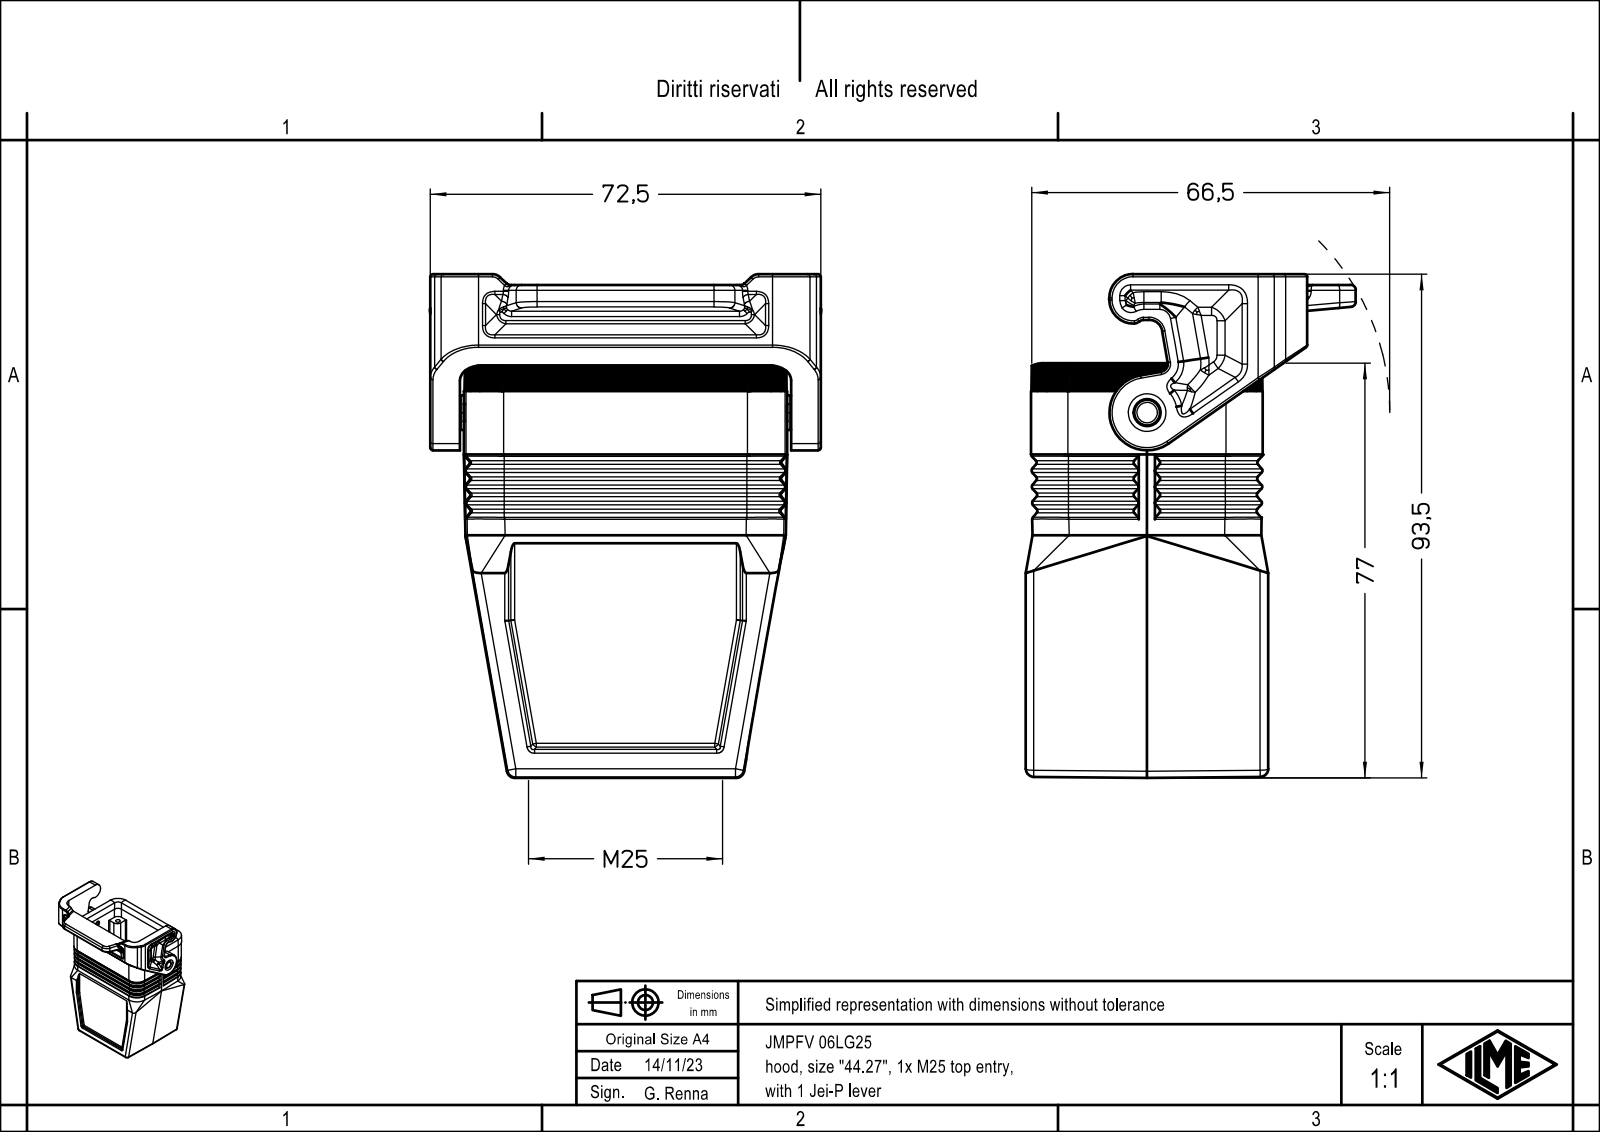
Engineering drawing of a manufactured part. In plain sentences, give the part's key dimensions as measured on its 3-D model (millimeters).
The part is named "JMPFV 06LG25". Its 3-D file was written by "Creo Elements/Direct Modeling 20.1B 02-Apr-2019 (C) Parametric Technology GmbH (AUTOMOTIVE_DESIGN)". It is 1 solid with 849 faces: 248 planar, 279 cylindrical and 322 other. Overall it measures 93.45 by 72.58 by 61.25 millimeters. Its volume is 82 789 cubic millimeters and its surface area 37 524 square millimeters. Round holes: 1 of diameter 23.6. Round bosses or shafts: 1 of diameter 6.4, 1 of diameter 4.8. Partial cylindrical surfaces (rounded edges, fillets, slot ends): 92 of radius 0.5, 47 of radius 1, 24 of radius 3, 22 of radius 1.5, 15 of radius 0.33, 13 of radius 7, 12 of radius 2, 8 of radius 4. The main face-to-face distances are 43, 1.03, 2, 3.25, 46.25, 7, 1, 44, 61.5, 85.45.
